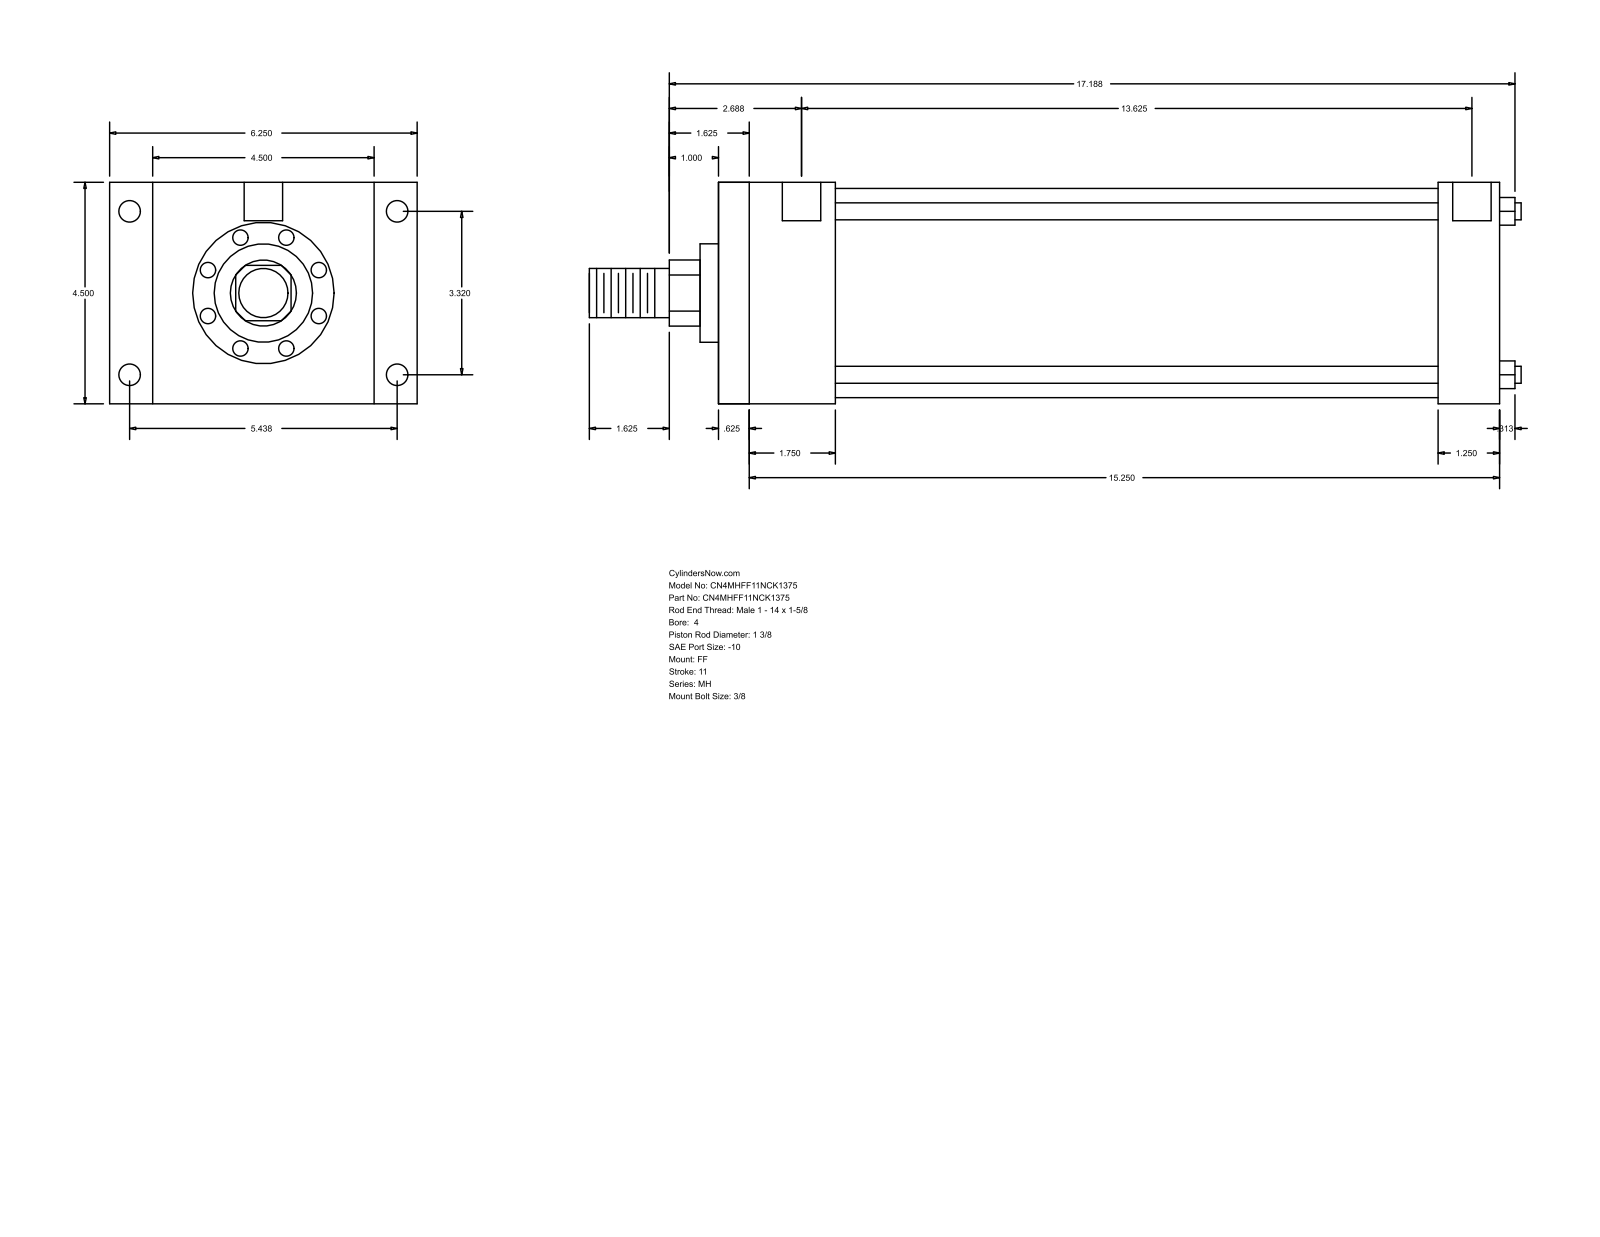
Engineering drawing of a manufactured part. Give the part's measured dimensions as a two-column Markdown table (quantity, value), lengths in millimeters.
| quantity | value |
| --- | --- |
| part name | MH_FF__0400_1.375 |
| STEP written by | GSSL Pune (CONFIG_CONTROL_DESIGN) |
| units | millimeters |
| bodies | 0 solids, 92 faces (64 planar, 28 cylindrical, 0 other) |
| overall size | 481.01 × 158.75 × 114.3 |
| round holes (diameter × count) | 8.73 × 4, 11.13 × 4, 19.84 × 2 |
| round bosses / shafts (diameter × count) | 8.76 × 4, 107.95 × 1, 50.8 × 1, 34.92 × 1, 25.4 × 1 |
| partial cylindrical surfaces (radius × count) | 17.06 × 1 |
| main face-to-face distances | 114.3, 403.22, 15.87, 387.35, 60.32, 44.45, 342.9, 371.48, 355.61, 311.16 |
| hole center spacings | 1.59, 84.32, 138.12, 161.82, 347.67, 349.26, 346.08 |
